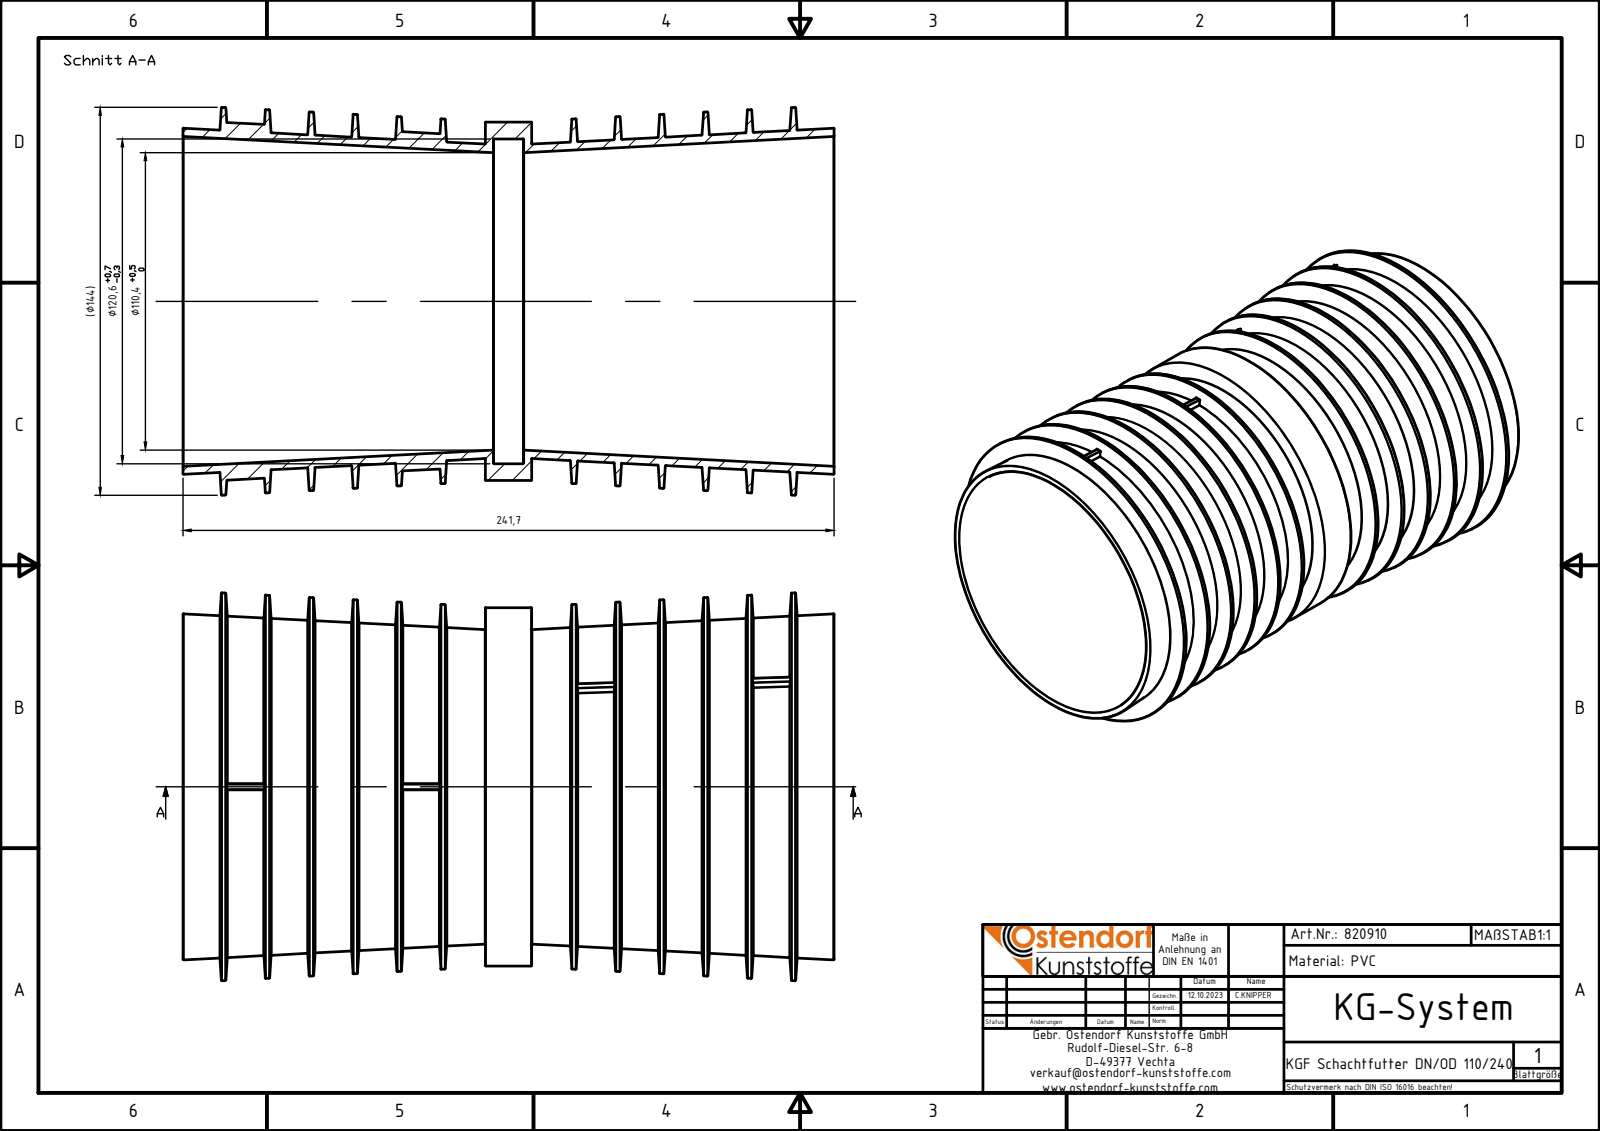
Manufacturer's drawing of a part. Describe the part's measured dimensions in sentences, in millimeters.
The part is named "820910z". Its 3-D file was written by "Autodesk Inventor 2024 (AUTOMOTIVE_DESIGN)". It is 1 solid with 284 faces: 30 planar, 18 cylindrical and 236 other. Overall it measures 241.7 by 143.98 by 143.98 millimeters. Its volume is 397 404 cubic millimeters and its surface area 273 728 square millimeters. Round holes: 1 of diameter 120.6. Round bosses or shafts: 1 of diameter 133. Partial cylindrical surfaces (rounded edges, fillets, slot ends): 16 of radius 0.2. The main face-to-face distances are 3, 14.2, 17.2, 112.25, 115.25, 126.45, 129.45, 11.2, 241.7, 2.2.
